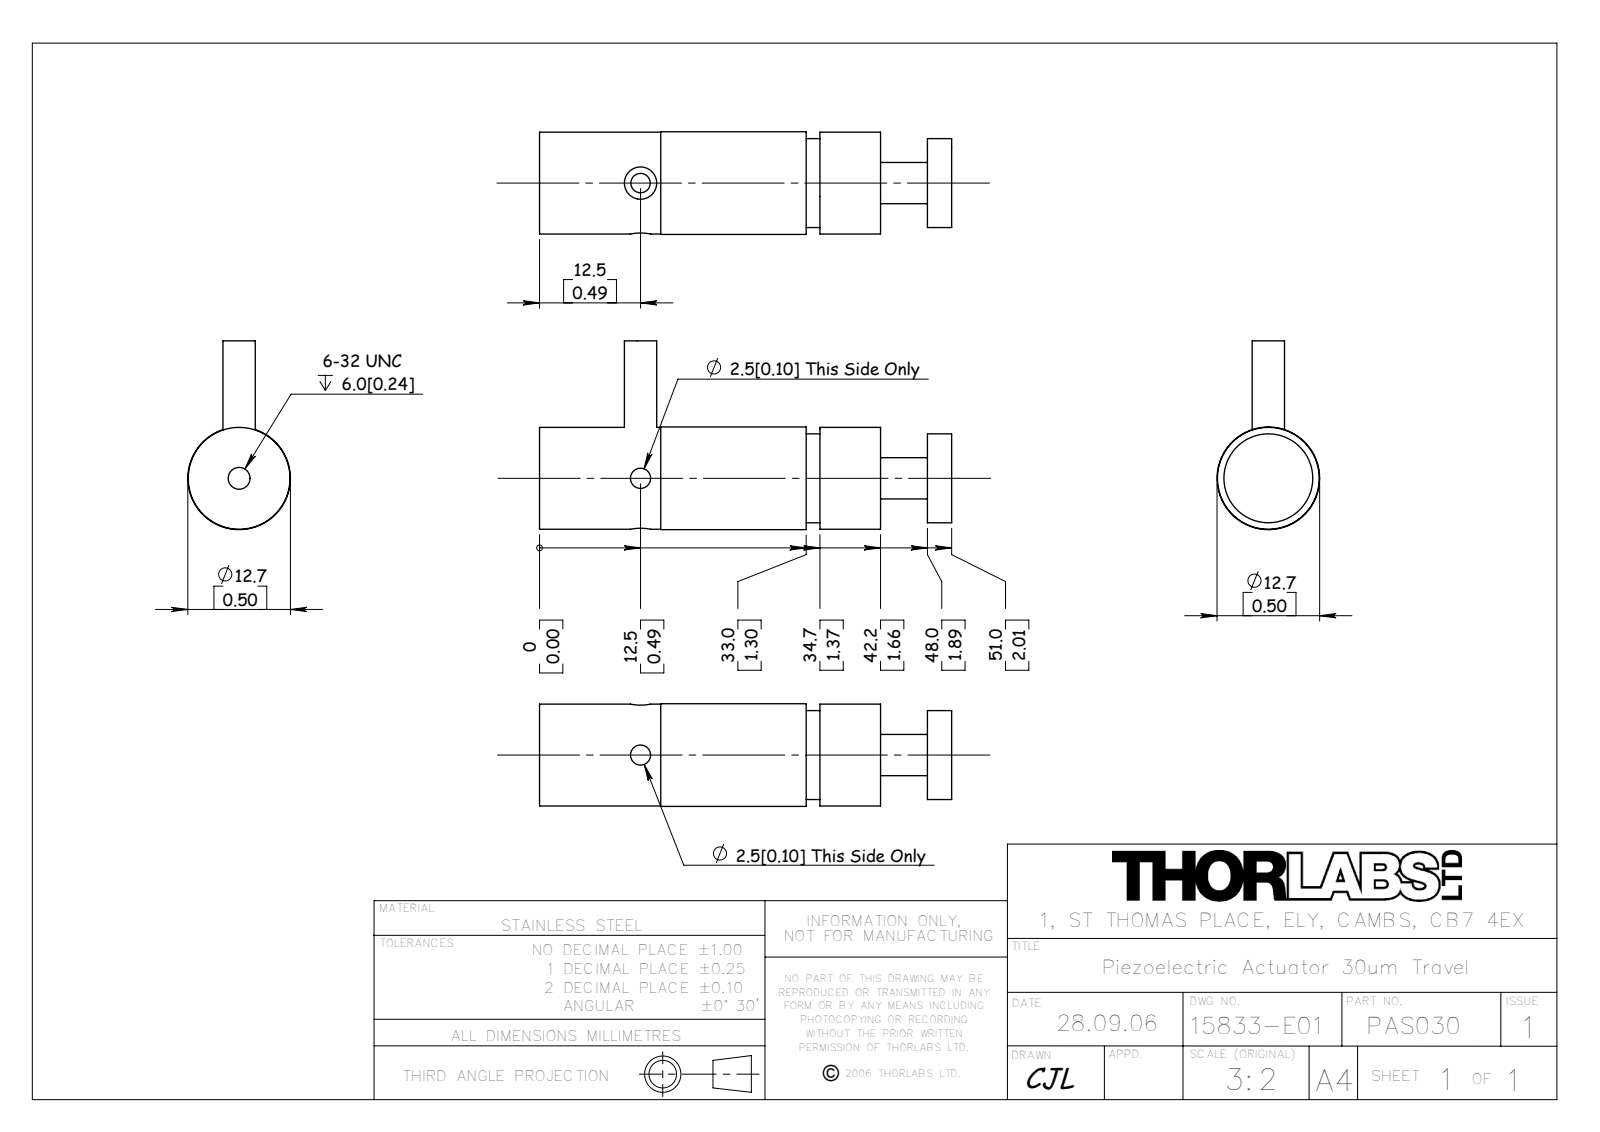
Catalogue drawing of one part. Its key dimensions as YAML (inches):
part_name: "15833-E0W"
step_written_by: "SolidWorks 2007 (AUTOMOTIVE_DESIGN)"
units: inches
bodies: {solids: 0, faces: 38, planar: 10, cylindrical: 28, other: 0}
overall_size: [2.008, 0.919, 0.5]
round_holes:
  - {diameter: 0.098, count: 2}
  - {diameter: 0.094, count: 1}
  - {diameter: 0.107, count: 1}
  - {diameter: 0.209, count: 1}
  - {diameter: 0.376, count: 1}
  - {diameter: 0.449, count: 1}
round_bosses_or_shafts:
  - {diameter: 0.5, count: 1}
  - {diameter: 0.496, count: 1}
  - {diameter: 0.433, count: 1}
  - {diameter: 0.201, count: 1}
  - {diameter: 0.157, count: 1}
face_to_face_distances: [1.661, 0.346, 2.008, 0.118, 0.228, 1.89, 0.591, 1.299, 1.614, 1.496]
